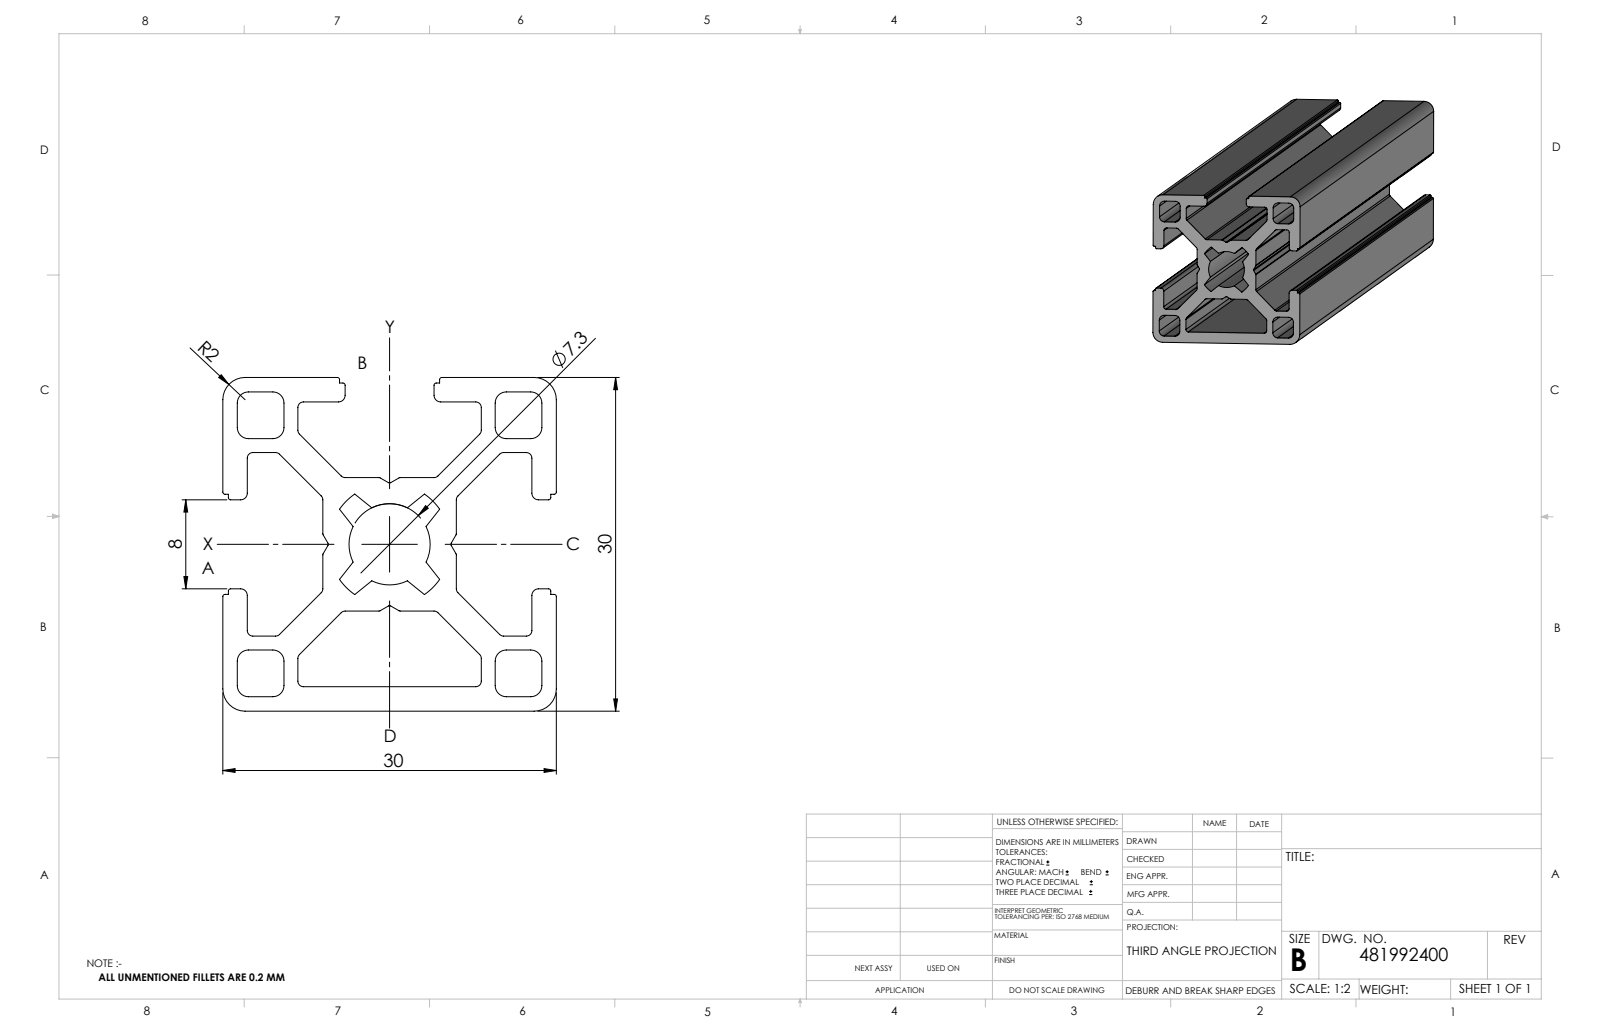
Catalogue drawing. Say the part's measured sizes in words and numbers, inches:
The part is named "481992400_c_1". Its 3-D file was written by "SolidWorks 2014 (CONFIG_CONTROL_DESIGN)". It is 1 solid with 174 faces: 90 planar, 84 cylindrical and 0 other. Overall it measures 7.874 by 1.181 by 1.181 inches. Its volume is 4.054 cubic inches and its surface area 107.3 square inches. Partial cylindrical surfaces (rounded edges, fillets, slot ends): 24 of radius 0.008, 24 of radius 0.02, 16 of radius 0.039, 6 of radius 0.024, 4 of radius 0.079, 1 of radius 0.144, 1 of radius 0.217. The main face-to-face distances are 1.094, 0.087, 1.181, 0.354, 0.827, 0.268, 0.74, 0.217, 0.1, 0.965.
